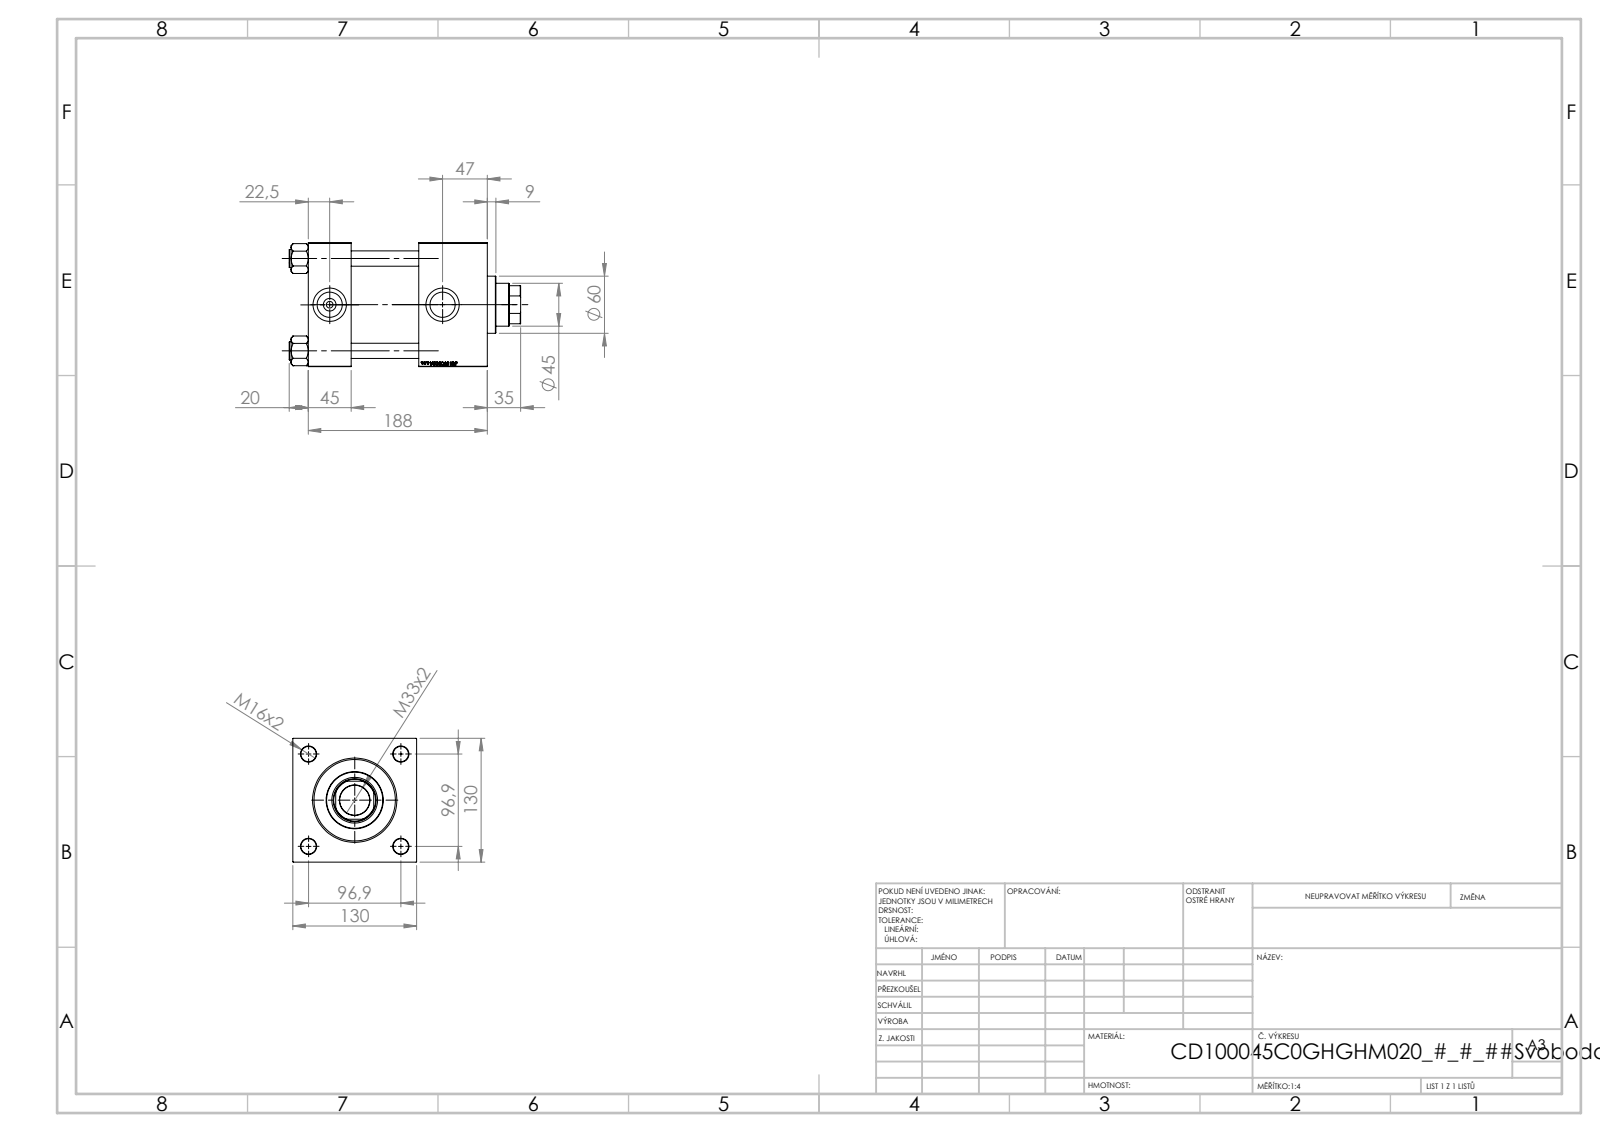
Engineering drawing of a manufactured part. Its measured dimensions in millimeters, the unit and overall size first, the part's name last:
Units: millimetres
Overall size (bounding box): 243 × 130 × 130
Round holes (diameter × count): ⌀16 ×4, ⌀7 ×2, ⌀26.44 ×2, ⌀35 ×2, ⌀31.5 ×1, ⌀45 ×1, ⌀48 ×1, ⌀76 ×1, ⌀85.5 ×1, ⌀100 ×1
Round bosses / shafts (diameter × count): ⌀19 ×4, ⌀106 ×1, ⌀60 ×1
Partial cylindrical surfaces — rounded edges, fillets, slot ends (radius × count): R22 ×1
Main face-to-face distances: 130, 45, 188, 143, 116, 71, 72, 20, 96, 51
Hole centre spacings: 68.52, 96.9, 137.04, 118.5
Volume: 2 425 000 mm³ · Surface area: 326 388 mm²
Bodies: 11 solids, 1196 faces (574 planar, 86 cylindrical, 536 other)
Part name (STEP PRODUCT): V215CD_VCP_C; V215CD_C_TYCINKA; V215CD_Body_C; V215CD_VC_C (+1 more)
STEP written by: SolidWorks 2019 (CONFIG_CONTROL_DESIGN)
